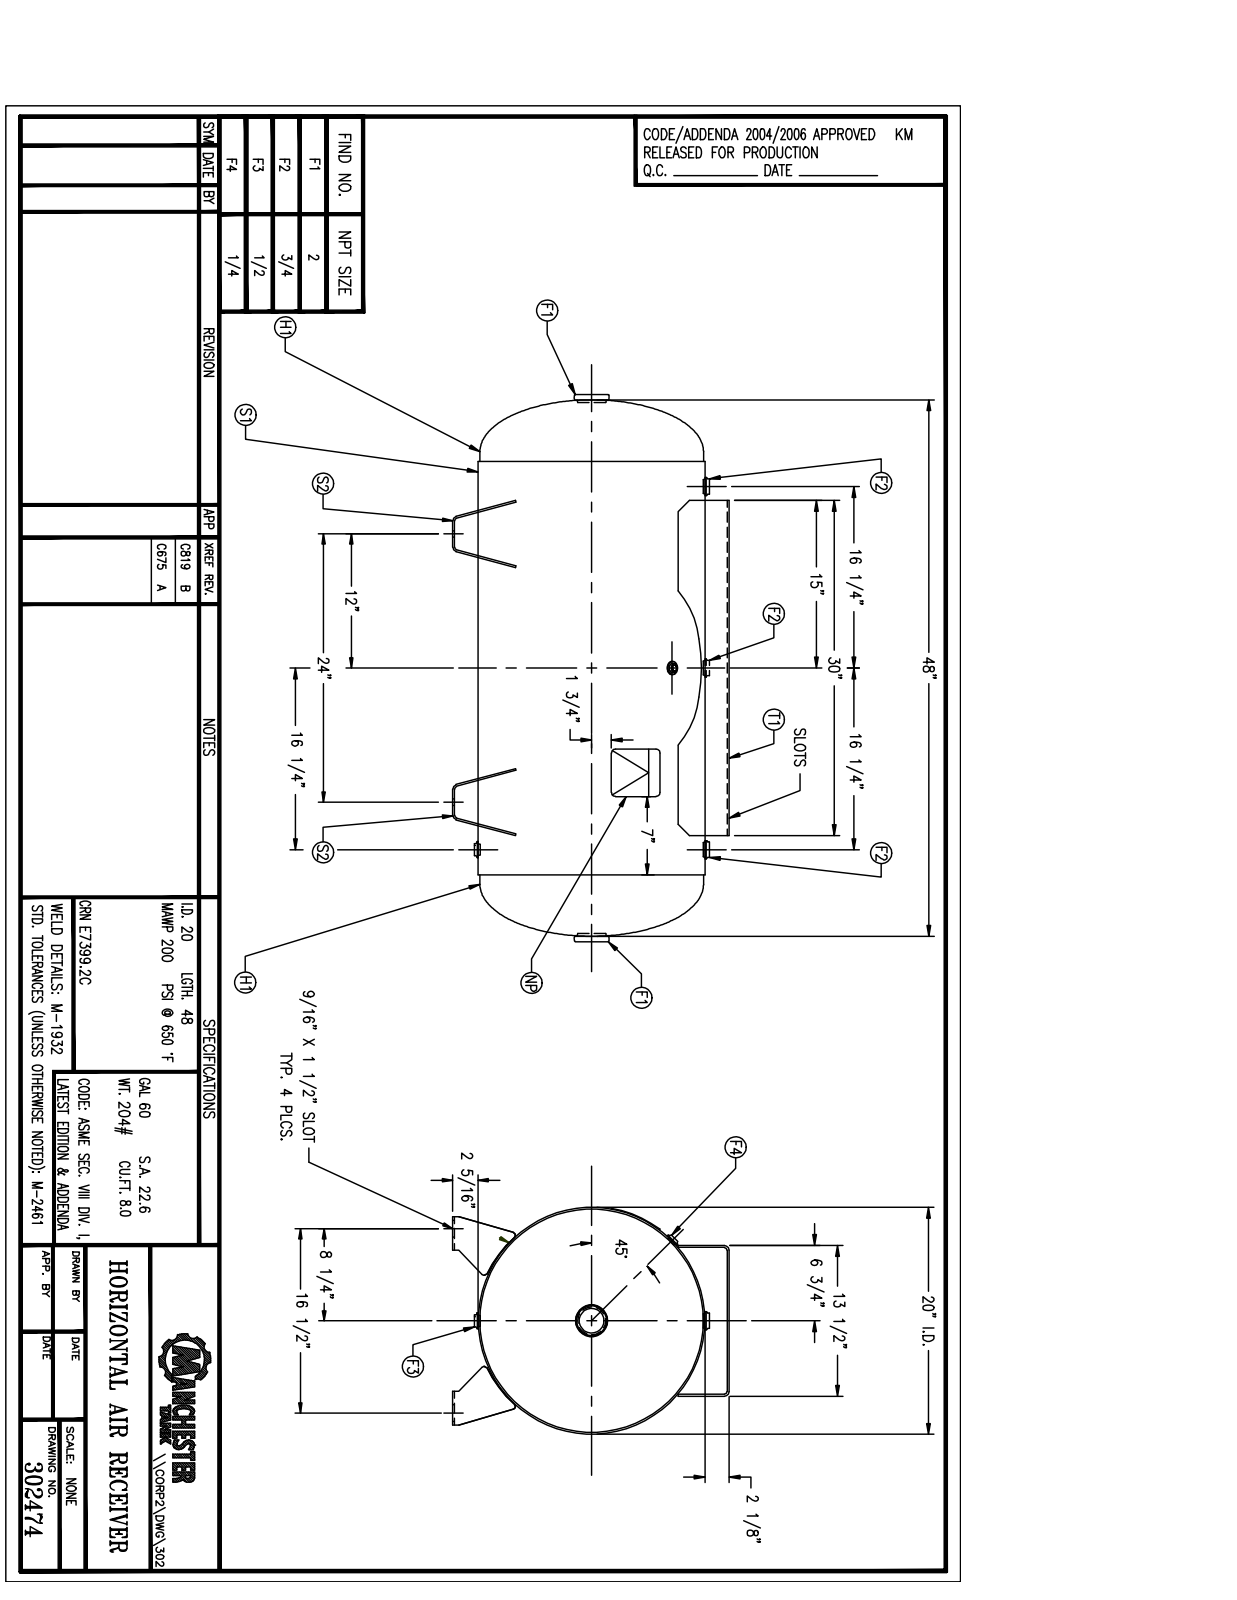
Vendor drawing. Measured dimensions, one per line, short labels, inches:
name: 302474
written by: SolidWorks 2011 (CONFIG_CONTROL_DESIGN)
unit: in
bodies: 0 solids, 340 faces (141 planar, 147 cylindrical, 52 other)
size: 49.156 × 24.776 × 20.308
holes: 2× ⌀1.05, 1× ⌀0.54, 1× ⌀0.84, 1× ⌀2.375, 1× ⌀3, 1× ⌀19.752
bosses: 2× ⌀1.63, 2× ⌀1.625, 2× ⌀1.45, 2× ⌀1.438, 1× ⌀20.308, 1× ⌀20, 1× ⌀3, 1× ⌀2.625
rounds: 20× R0.203, 20× R0.25, 8× R0.281, 8× R10.125, 4× R0.415, 2× R0.242, 2× R0.429, 2× R7.897
face distances: 0.187, 13.313, 0.165, 13.5, 13.126, 23.184, 23.019, 0.164, 23.183, 23.184
hole spacings: 16.25, 32.5
